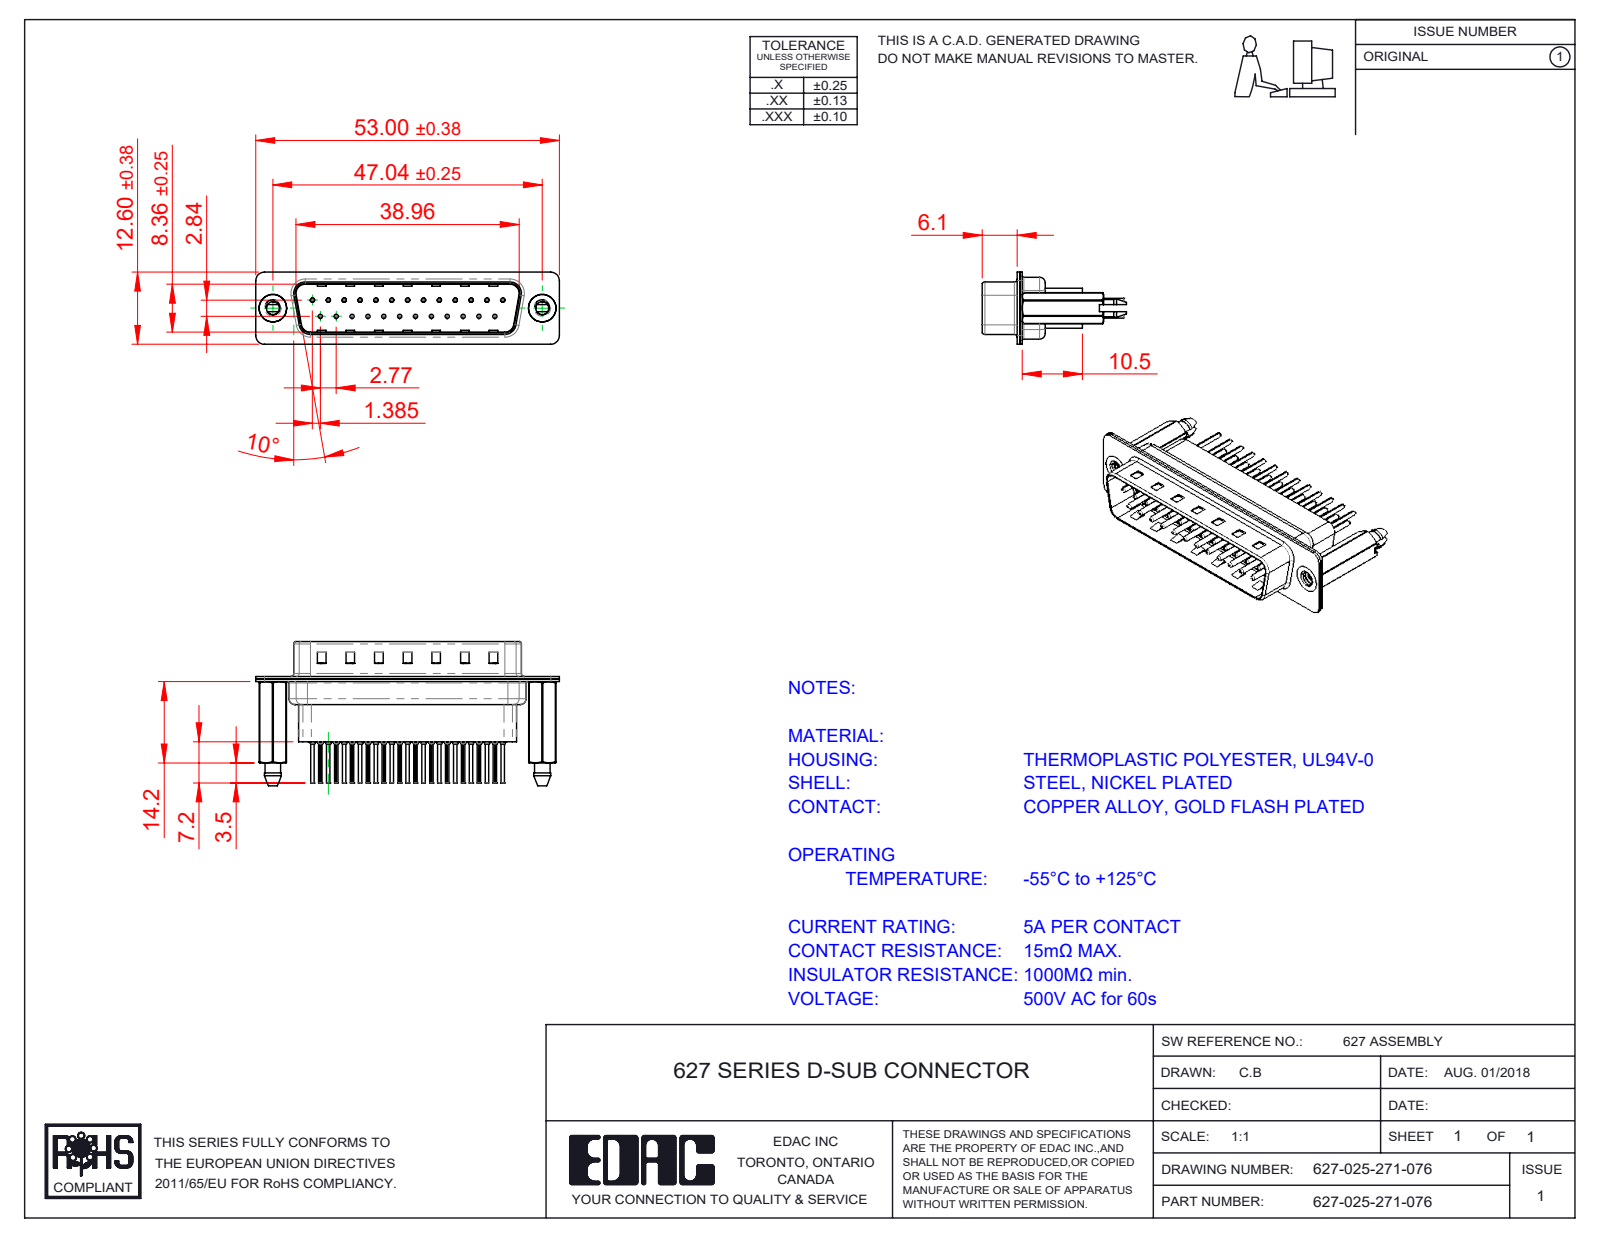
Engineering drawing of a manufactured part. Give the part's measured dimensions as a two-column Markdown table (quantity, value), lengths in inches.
| quantity | value |
| --- | --- |
| part name | 627 Shell Front_25 Contacts; 627 Contact Row 1_61; 627 Housing_25 HP; 627 Shell Rear_25 Contacts (+3 more) |
| STEP written by | SolidWorks 2020 (CONFIG_CONTROL_DESIGN) |
| units | inches |
| bodies | 30 solids, 2934 faces (803 planar, 1128 cylindrical, 1003 other) |
| overall size | 2.087 × 0.988 × 0.496 |
| volume | 0.255 in³ |
| surface area | 16.73 in² |
| round holes (diameter × count) | 0.008 × 25, 0.014 × 25, 0.043 × 25, 0.063 × 25, 0.089 × 2, 0.157 × 2, 0.189 × 2 |
| round bosses / shafts (diameter × count) | 0.079 × 25, 0.059 × 25, 0.03 × 25, 0.024 × 25, 0.193 × 2 |
| partial cylindrical surfaces (radius × count) | 0.004 × 50, 0.059 × 18, 0.079 × 12, 0.063 × 10, 0.02 × 8, 0.01 × 4, 0.024 × 4, 0.026 × 4 |
| main face-to-face distances | 0.016, 0.018, 0.032, 0.377, 0.027, 0.302, 0.059, 0.035, 0.043, 0.318 |
| hole center spacings | 0.124, 0.327, 0.109, 0.218, 0.436, 0.654, 0.198, 0.198 |
